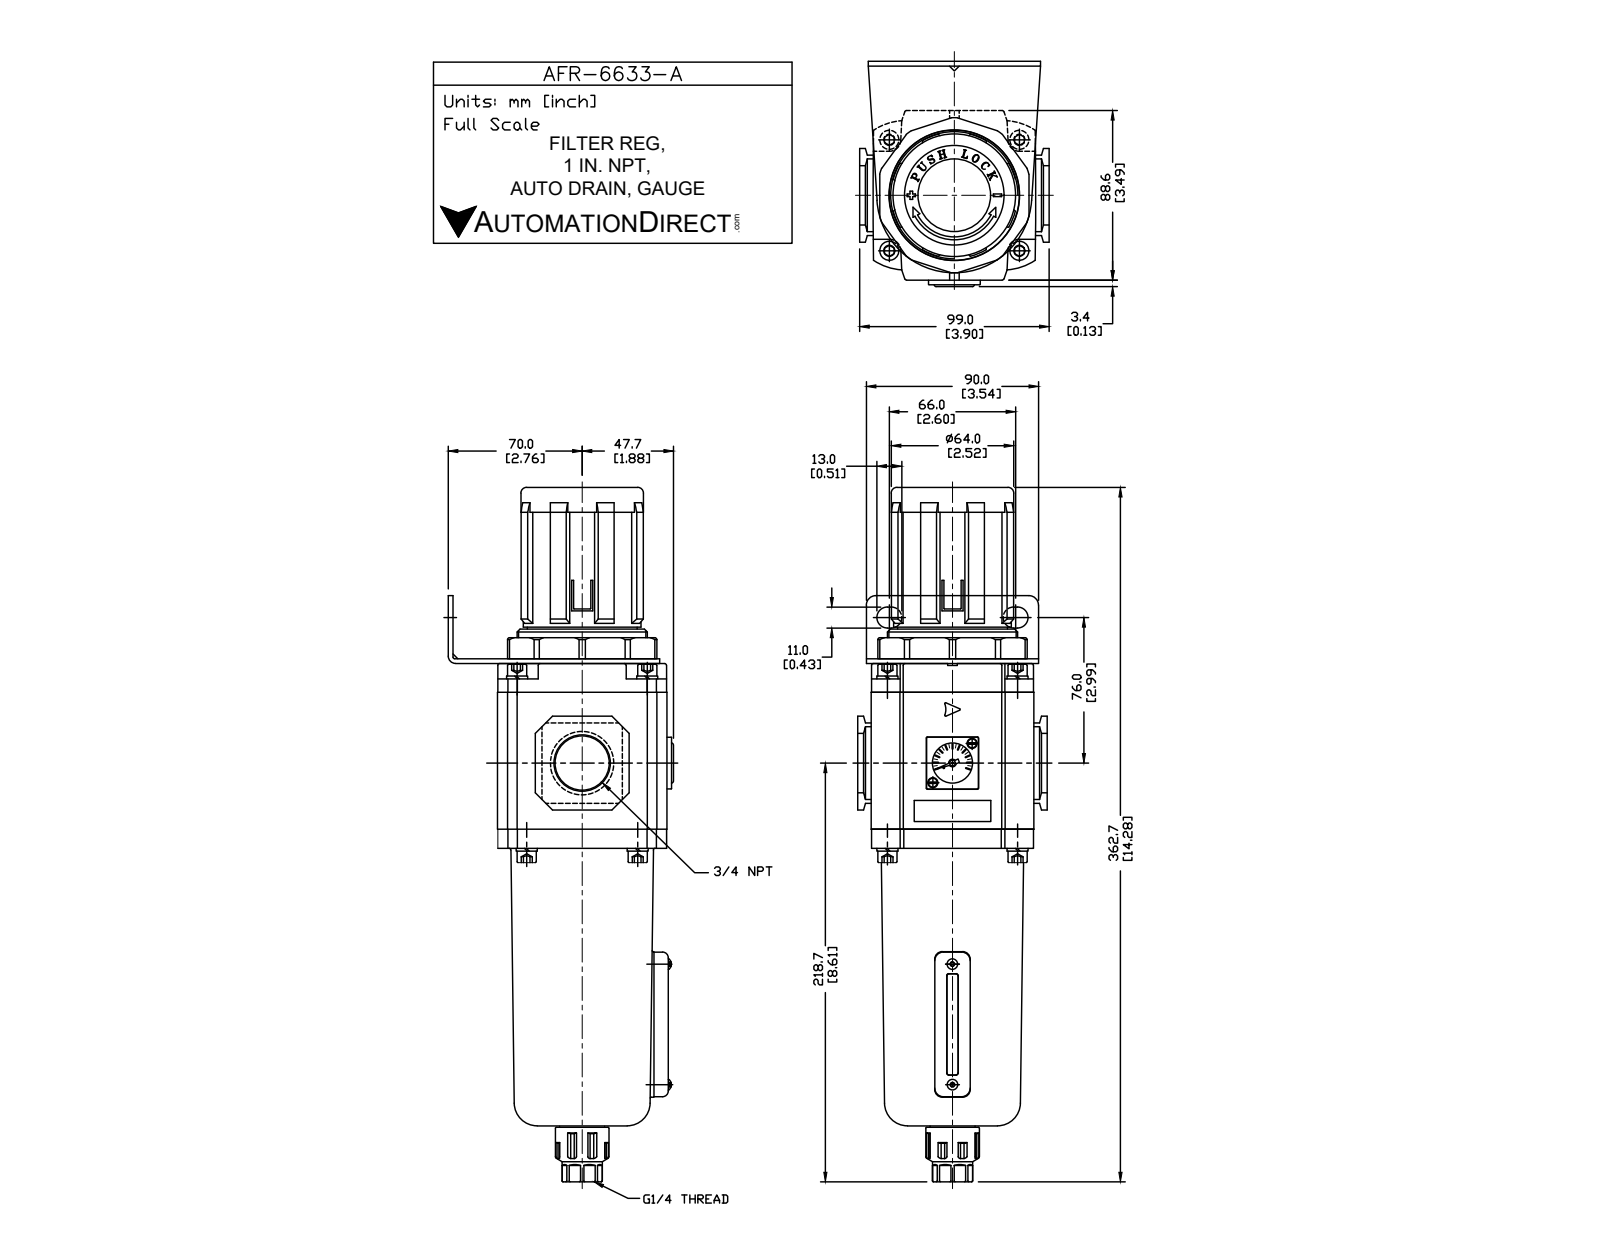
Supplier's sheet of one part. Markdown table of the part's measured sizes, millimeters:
| quantity | value |
| --- | --- |
| part name | AFR-6633-A |
| STEP written by | SolidWorks 2015 (CONFIG_CONTROL_DESIGN) |
| units | millimeters |
| bodies | 16 solids, 703 faces (439 planar, 175 cylindrical, 89 other) |
| overall size | 362.7 × 117 × 99 |
| volume | 1 686 000 mm³ |
| surface area | 184 625 mm² |
| round holes (diameter × count) | 3 × 6, 2 × 1, 12 × 1, 23.01 × 1, 30 × 1, 38 × 1 |
| round bosses / shafts (diameter × count) | 10 × 8, 5.5 × 2, 2.7 × 2, 68 × 1, 64 × 1, 62 × 1, 53.76 × 1, 28 × 1 |
| partial cylindrical surfaces (radius × count) | 1 × 12, 1.2 × 10, 1.3 × 8, 2.5 × 8, 9.5 × 8, 19.9 × 8, 0.5 × 6, 0.3 × 4 |
| main face-to-face distances | 2.5, 91.2, 88.7, 87.6, 1, 88.6, 92, 85, 10, 7 |
| hole center spacings | 41.35, 34.68, 53.16, 63.36, 82.71, 69.35 |
